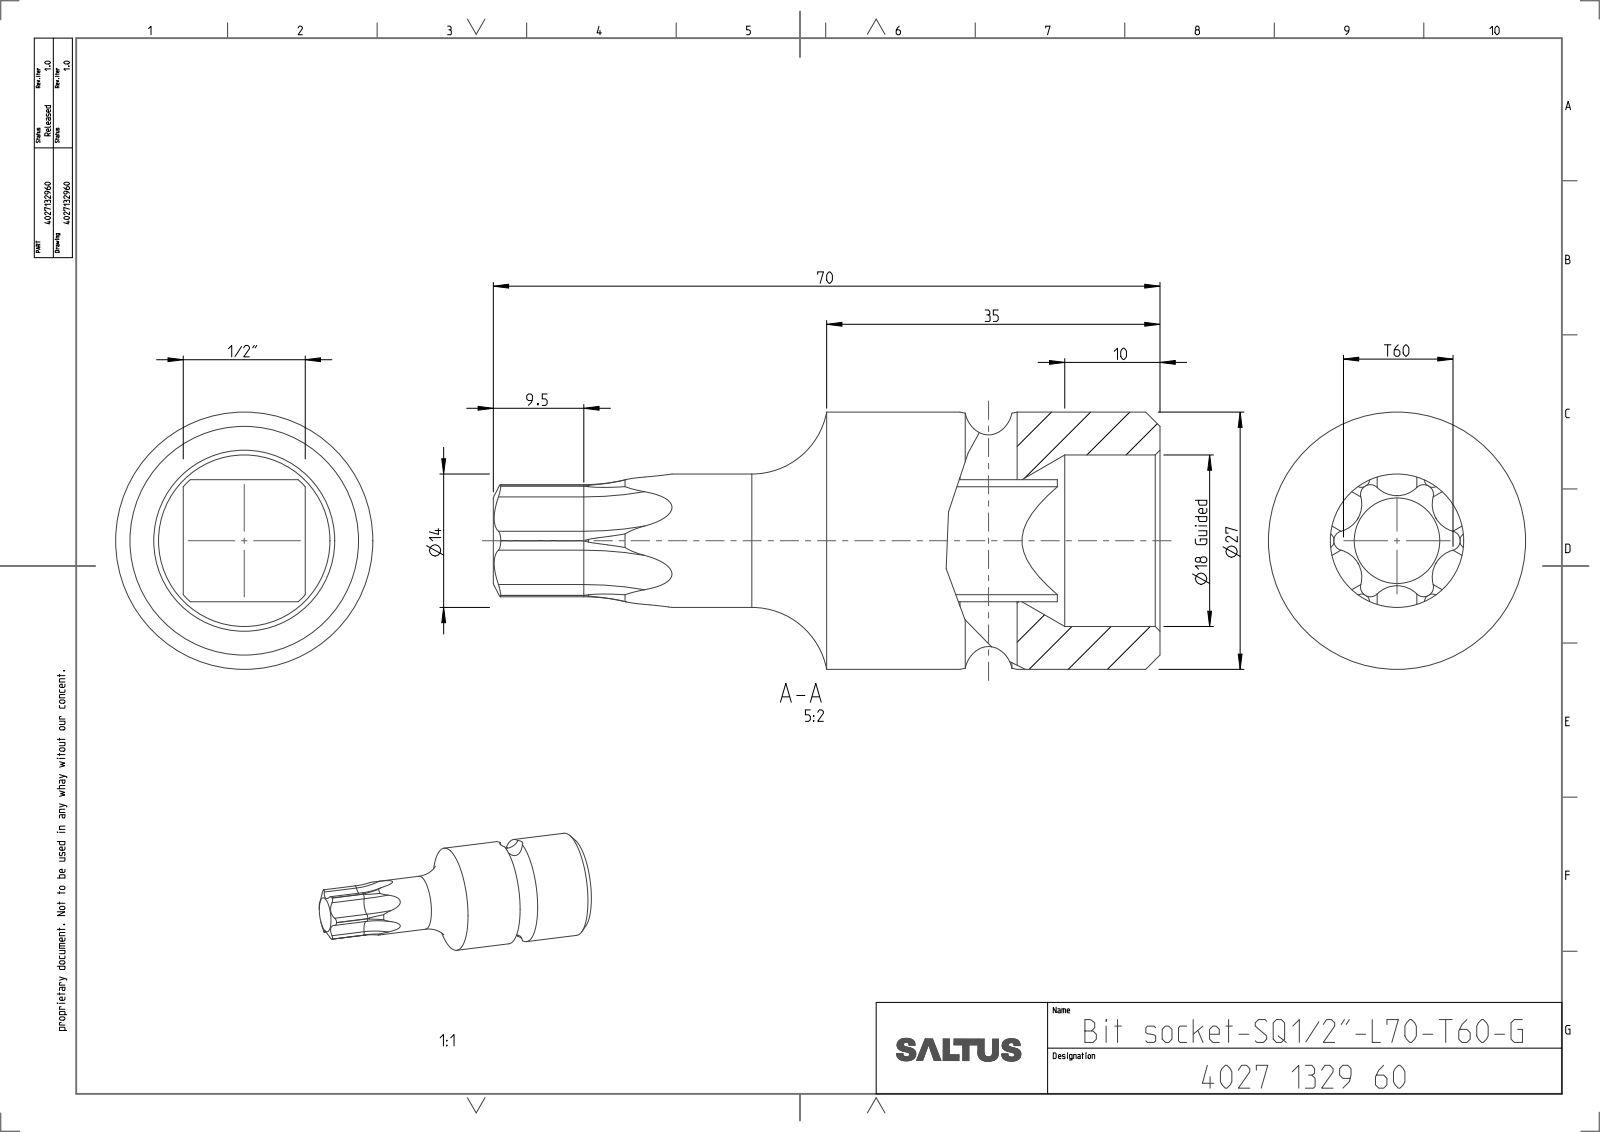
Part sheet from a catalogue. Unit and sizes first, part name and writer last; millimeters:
Units: millimetres
Overall size (bounding box): 70 × 27 × 27
Round holes (diameter × count): ⌀6 ×1, ⌀18 ×1
Round bosses / shafts (diameter × count): ⌀27 ×1, ⌀14 ×1
Partial cylindrical surfaces — rounded edges, fillets, slot ends (radius × count): R1.01 ×12, R2.94 ×6, R6.63 ×1, R8.55 ×1
Main face-to-face distances: 12.82, 26, 70, 44
Volume: 18 948 mm³ · Surface area: 6 897 mm²
Bodies: 1 solid, 83 faces (7 planar, 40 cylindrical, 36 other)
Part name (STEP PRODUCT): 4027132960
STEP written by: CREO PARAMETRIC BY PTC INC, 2022414 (CONFIG_CONTROL_DESIGN)
